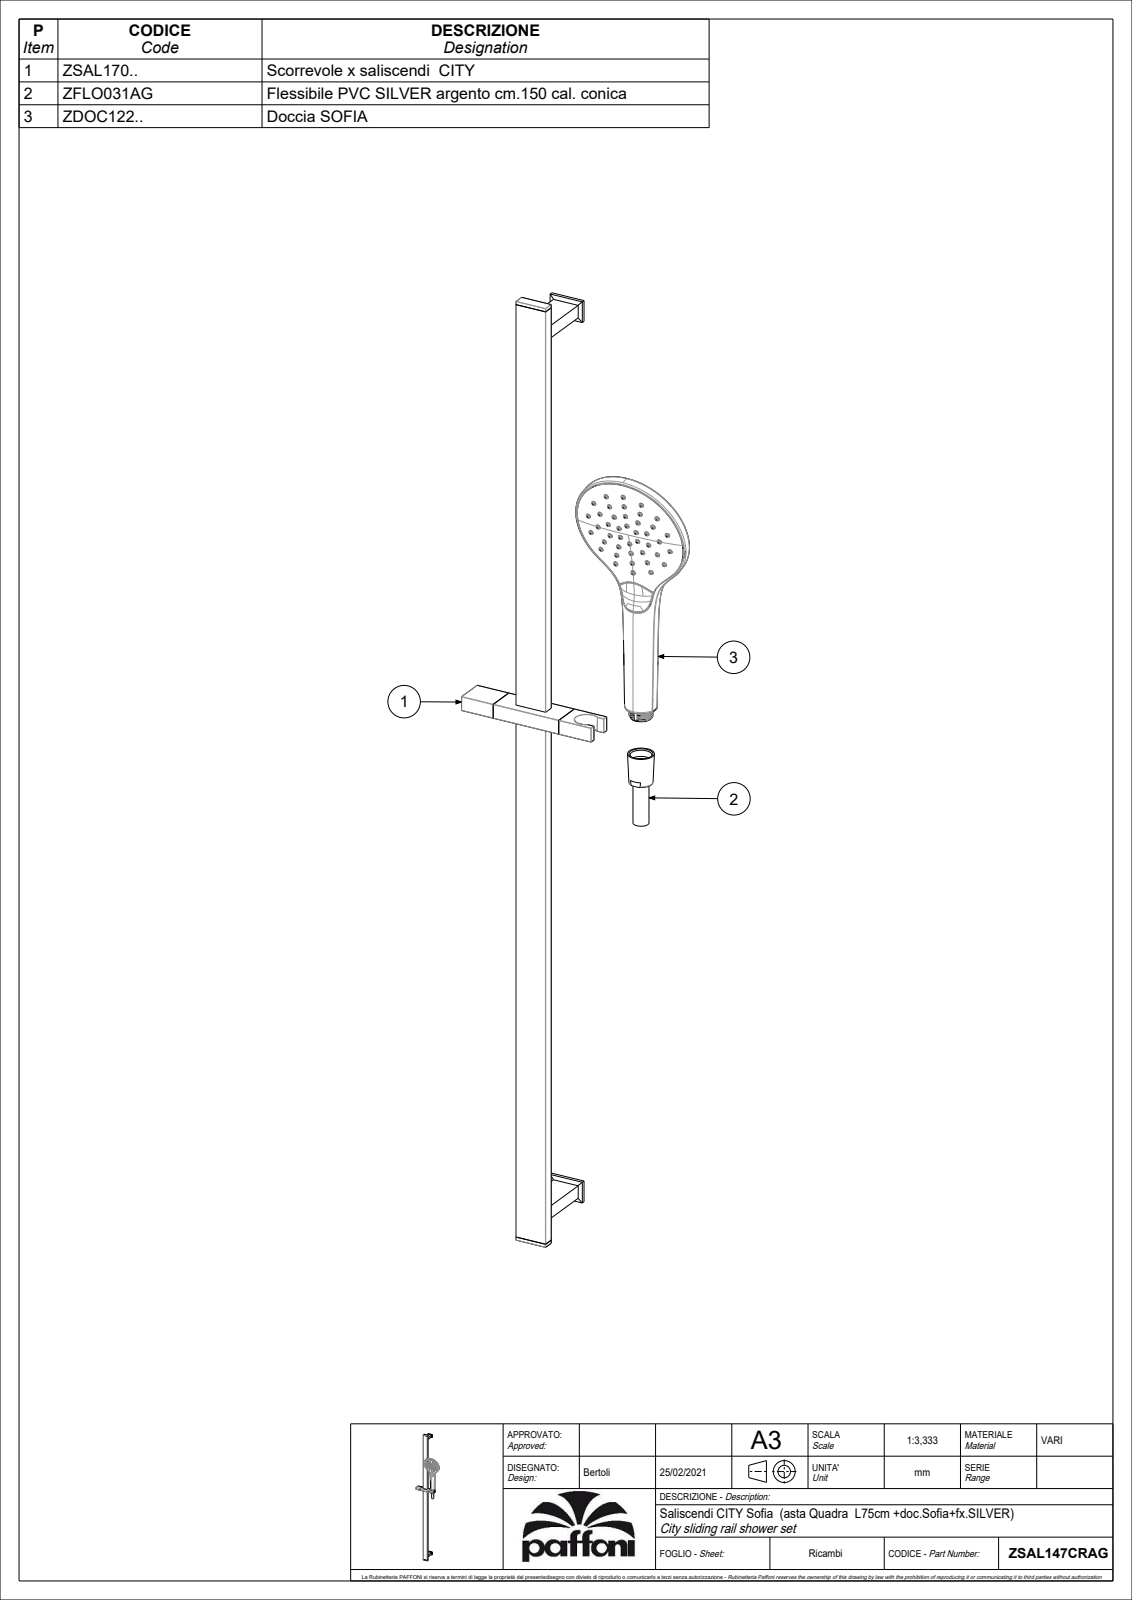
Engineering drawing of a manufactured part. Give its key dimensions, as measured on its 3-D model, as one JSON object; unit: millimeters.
{"part_name": "4071543CR; 4071389AGE; 4071084CR_E; 4071084CR_A (+8 more)", "step_written_by": "CREO PARAMETRIC BY PTC INC, 2020044 (CONFIG_CONTROL_DESIGN)", "units": "millimeters", "bodies": {"solids": 11, "faces": 2792, "planar": 589, "cylindrical": 447, "other": 1756}, "overall_size": [906.4, 173.37, 92.66], "volume_mm3": 393697, "surface_area_mm2": 190627, "round_holes": [[6, 4], [4, 3], [10, 2], [0.7, 1], [2.7, 1], [3, 1], [6.6, 1], [9.4, 1], [10.36, 1], [11, 1], [11.4, 1], [12, 1]], "round_bosses_or_shafts": [[7, 4], [24.8, 1], [22.92, 1], [20.5, 1], [18.64, 1], [18.5, 1], [16.5, 1], [14.2, 1]], "partial_cylinders_radius": [[0.2, 56], [0.5, 40], [0.3, 39], [1, 23], [19, 12], [18.5, 8], [1.5, 5], [0.4, 4]], "face_to_face_distances": [10, 30, 27.5, 18.75, 8.75, 13.5, 12, 2.5, 850, 46.25], "hole_center_spacings": [36, 15.93, 20.31, 24.87, 37.41, 38.65, 44.92, 48]}
